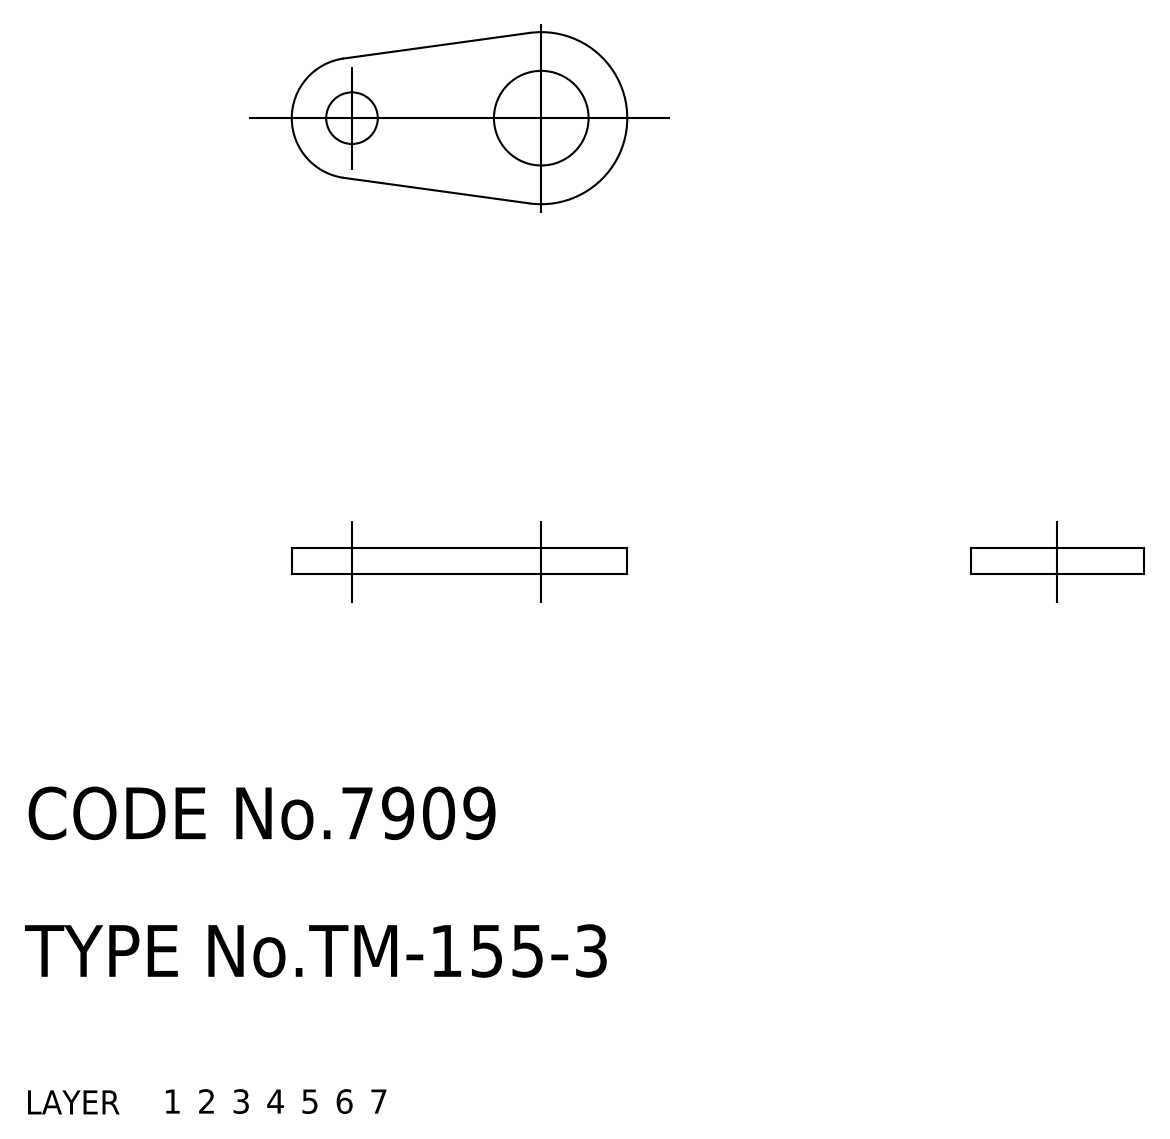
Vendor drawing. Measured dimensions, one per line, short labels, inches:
name: terminal
written by: CADfix (AUTOMOTIVE_DESIGN)
unit: in
bodies: 1 solid, 10 faces (0 planar, 0 cylindrical, 10 other)
size: 0.768 × 0.394 × 0.059
volume: 0.011 in³; area: 0.555 in²
